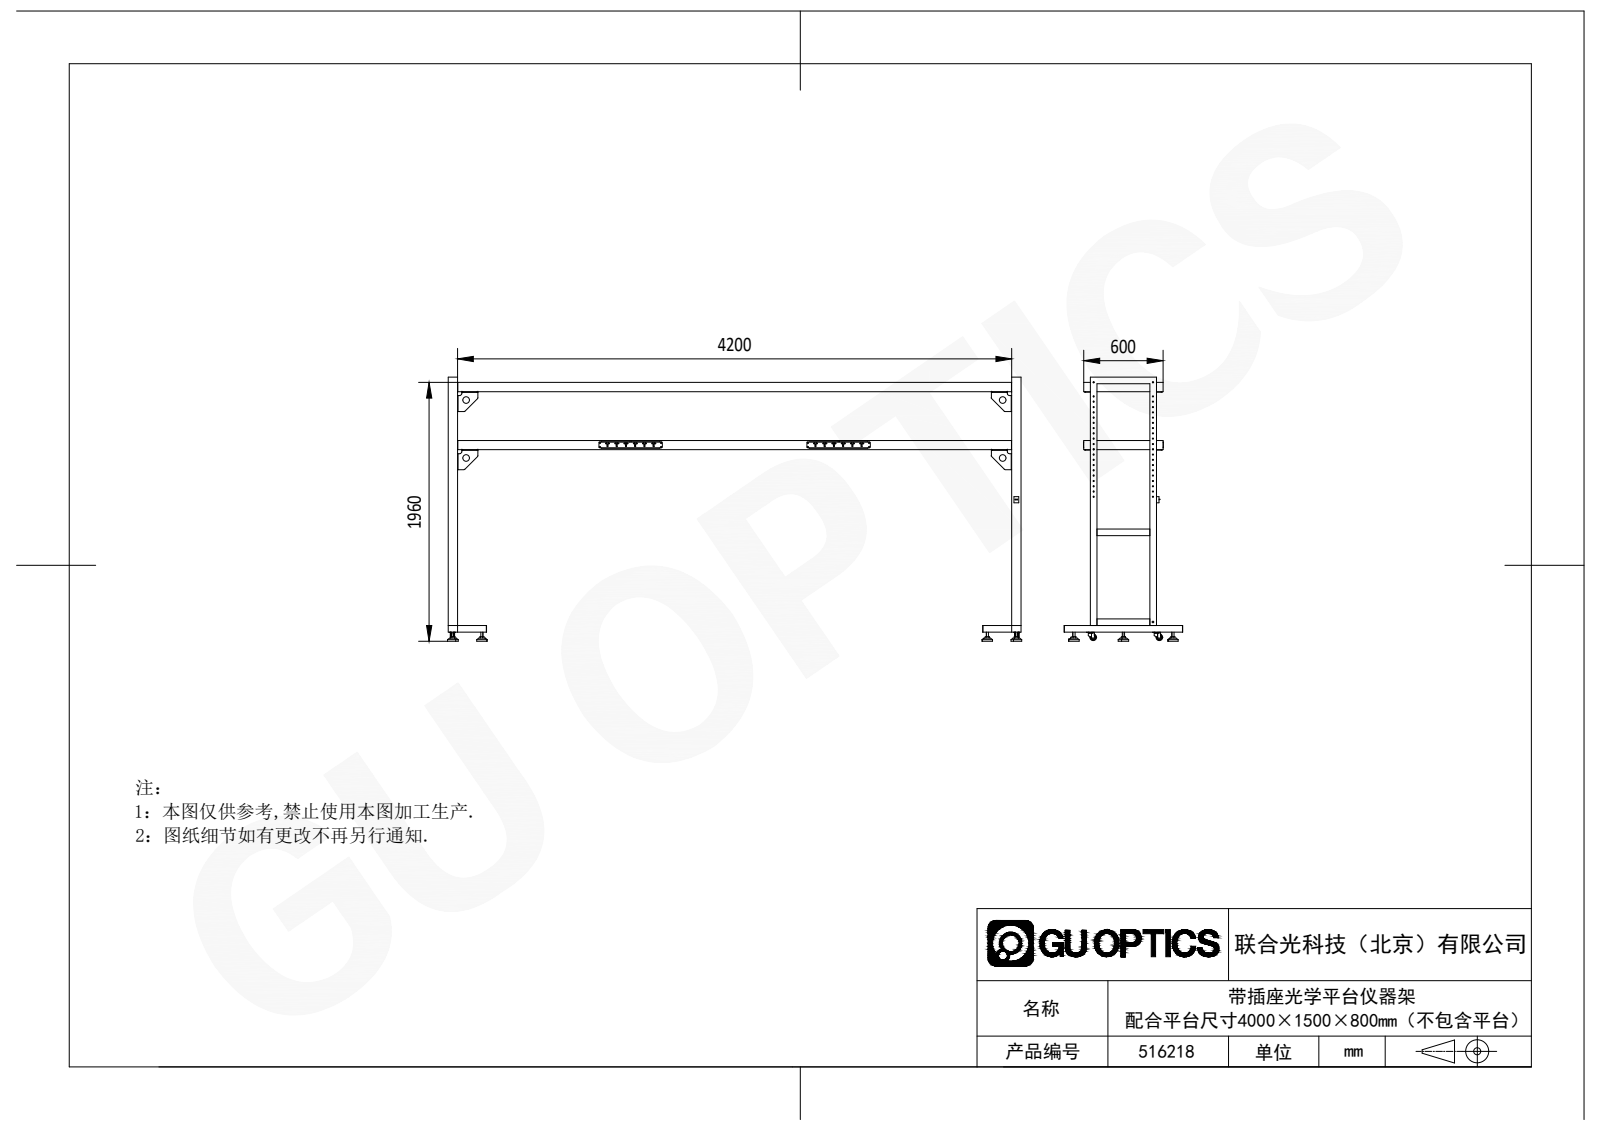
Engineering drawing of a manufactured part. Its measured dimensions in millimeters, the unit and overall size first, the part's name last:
Units: millimetres
Overall size (bounding box): 4350 × 2001 × 900
Round holes (diameter × count): ⌀9 ×66, ⌀6.1 ×16, ⌀10 ×16, ⌀6.5 ×12, ⌀4.2 ×8, ⌀5.2 ×8, ⌀6 ×8, ⌀17 ×6, ⌀18 ×6, ⌀26 ×6, ⌀69 ×6, ⌀3.2 ×4
Round bosses / shafts (diameter × count): ⌀80 ×6, ⌀16 ×6, ⌀26 ×4, ⌀18 ×4, ⌀50 ×2, ⌀10 ×2
Partial cylindrical surfaces — rounded edges, fillets, slot ends (radius × count): R5 ×36, R7 ×24, R3 ×16, R4.25 ×12, R1.5 ×8, R1.51 ×8, R4.01 ×8, R13 ×4
Main face-to-face distances: 440, 1.5, 3, 70, 67, 438.5, 2.5, 67.5, 441.5, 530
Hole centre spacings: 40, 80, 120, 280, 160, 200, 240, 320
Volume: 32 430 000 mm³ · Surface area: 24 370 000 mm²
Bodies: 55 solids, 2593 faces (1445 planar, 1072 cylindrical, 76 other)
Part name (STEP PRODUCT): 516218
STEP written by: SolidWorks 2020 (CONFIG_CONTROL_DESIGN)
